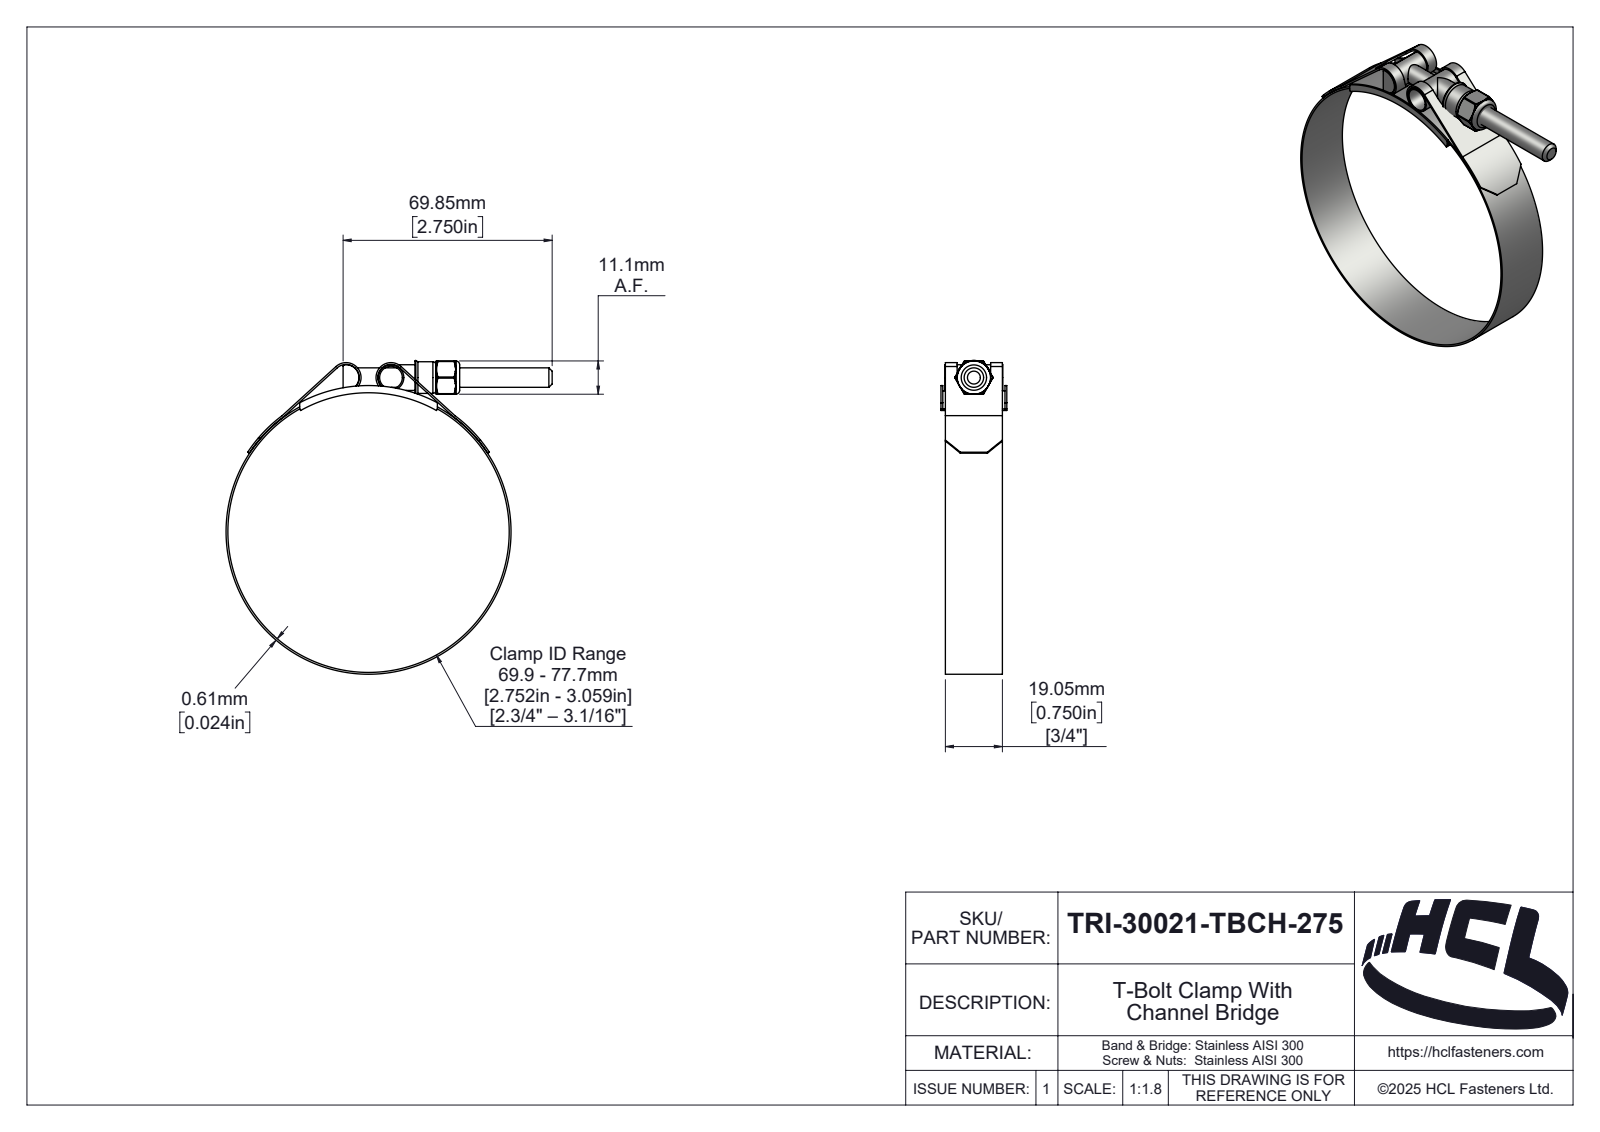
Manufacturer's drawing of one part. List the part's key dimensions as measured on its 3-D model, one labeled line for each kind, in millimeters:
Part name (STEP PRODUCT): TRI-30021-TBCH-275
STEP written by: SolidWorks 2025 (AUTOMOTIVE_DESIGN)
Units: millimetres
Bodies: 6 solids, 330 faces (46 planar, 122 cylindrical, 162 other)
Overall size (bounding box): 108.96 × 104.79 × 22
Volume: 9 210 mm³ · Surface area: 21 487 mm²
Round holes (diameter × count): ⌀5.4 ×1, ⌀6.35 ×1, ⌀6.5 ×1, ⌀7.58 ×1, ⌀94 ×1
Round bosses / shafts (diameter × count): ⌀8.58 ×2, ⌀95.22 ×1, ⌀10.58 ×1
Partial cylindrical surfaces — rounded edges, fillets, slot ends (radius × count): R0.39 ×6, R0.5 ×2, R4.39 ×2, R5 ×2, R0.59 ×1, R2.42 ×1, R3.03 ×1, R3.19 ×1
Main face-to-face distances: 0.61, 19.06, 1.47, 20.53, 21.39, 0.86, 19.92, 0.74, 22, 11.11
Hole centre spacings: 52
